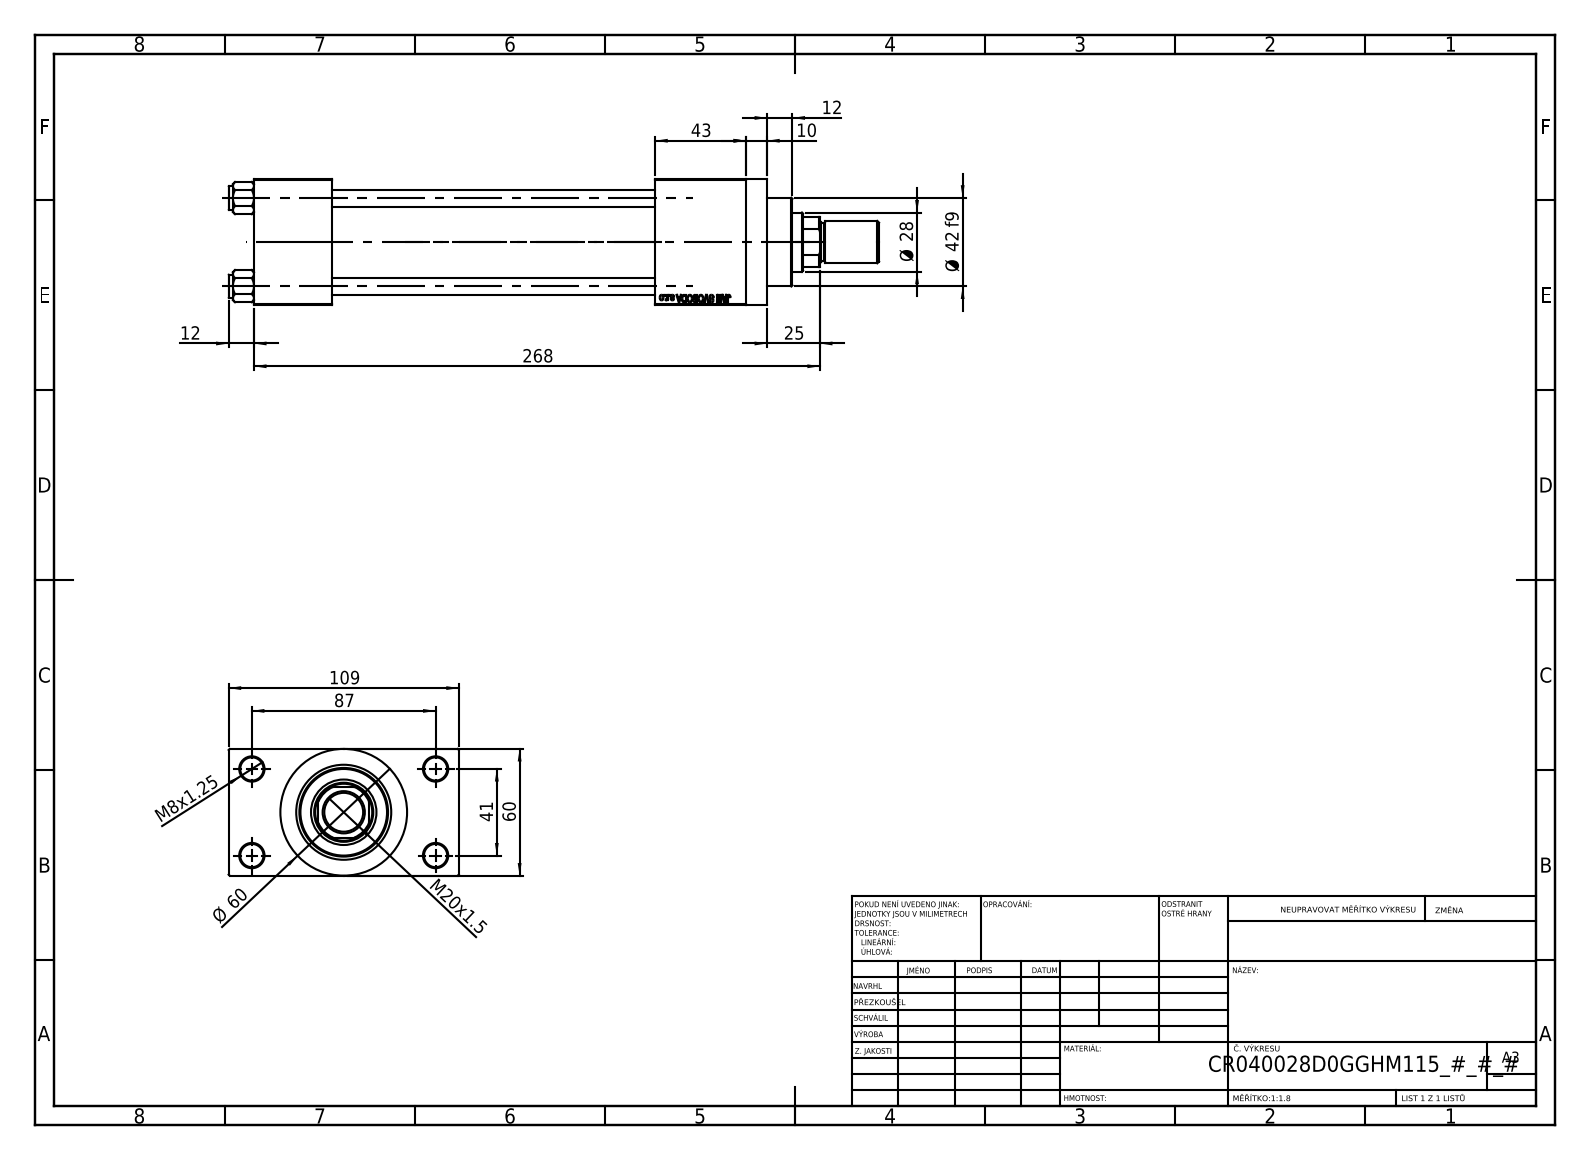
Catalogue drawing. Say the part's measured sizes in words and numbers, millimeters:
The part is named "V215CR_VCP_D; V215CR_D_TYCINKA; ROD_END_AH; V215_VC_A (+2 more)". Its 3-D file was written by "SolidWorks 2019 (CONFIG_CONTROL_DESIGN)". It is 12 solids with 1119 faces: 502 planar, 93 cylindrical and 524 other. Overall it measures 308 by 109 by 60 millimeters. Its volume is 658 871 cubic millimeters and its surface area 173 834 square millimeters. Round holes: 4 of diameter 8, 4 of diameter 11, 2 of diameter 7, 2 of diameter 16.66, 2 of diameter 24, 1 of diameter 18.5, 1 of diameter 28, 1 of diameter 31, 1 of diameter 40, 1 of diameter 45. Round bosses or shafts: 4 of diameter 11, 1 of diameter 60, 1 of diameter 46, 1 of diameter 42, 1 of diameter 20, 1 of diameter 18. Partial cylindrical surfaces (rounded edges, fillets, slot ends): 1 of radius 13.5. The main face-to-face distances are 60, 24.5, 84.5, 153, 37, 190, 233, 196, 43, 109. The hole center spacings are 22.65, 29.49, 41.7, 47.15, 48.09, 64.35, 76.49, 41.
